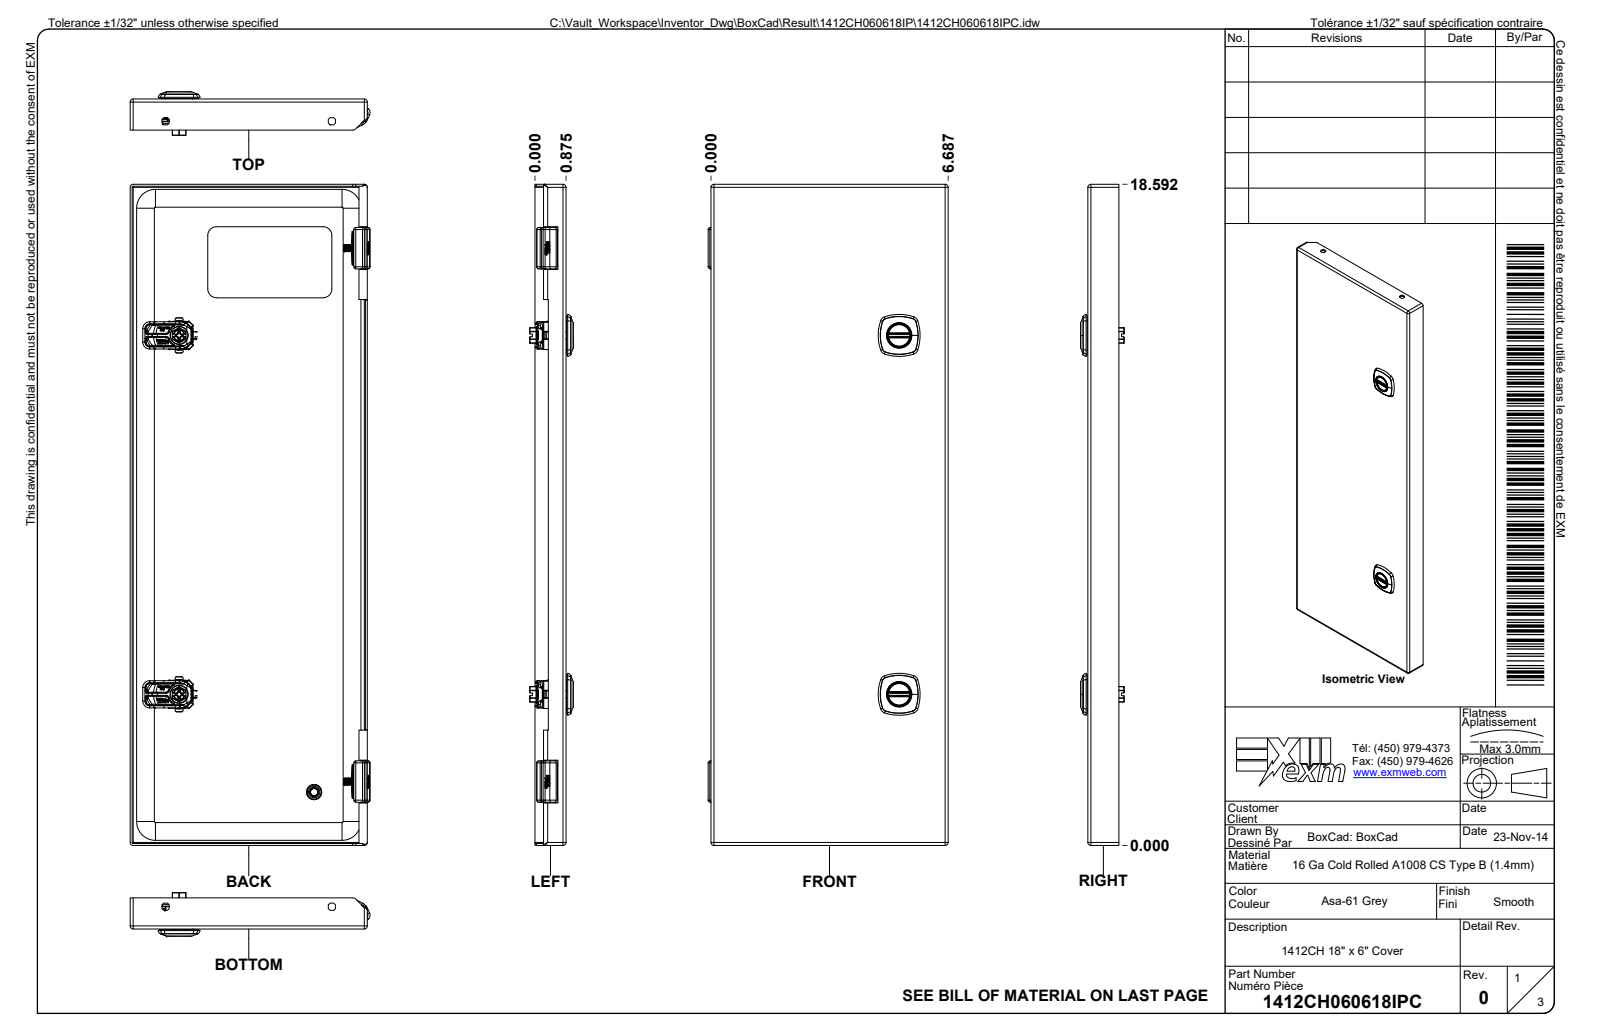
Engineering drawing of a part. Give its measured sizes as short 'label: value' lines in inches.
name: 1412CH060618IP; 1412CH060618IPB; 1412CH060618IPB-P; STK-Q-08350 (+8 more)
written by: Autodesk Inventor 2024 (AUTOMOTIVE_DESIGN)
unit: in
bodies: 67 solids, 9235 faces (4701 planar, 1930 cylindrical, 2604 other)
size: 18.592 × 7.496 × 6.451
volume: 42.74 in³; area: 1 447 in²
holes: 13× ⌀0.201, 6× ⌀0.03, 6× ⌀0.24, 6× ⌀0.311, 4× ⌀0.305, 4× ⌀0.32, 4× ⌀0.394, 2× ⌀0.165, 2× ⌀0.173, 2× ⌀0.175, 2× ⌀0.236, 2× ⌀0.63
bosses: 10× ⌀0.232, 6× ⌀0.512, 6× ⌀0.035, 4× ⌀0.39, 3× ⌀0.197, 2× ⌀0.799, 2× ⌀0.626, 2× ⌀0.504
rounds: 293× R0.02, 105× R0.01, 94× R0.008, 91× R0.012, 82× R0.039, 53× R0.004, 31× R0.079, 31× R0.197
face distances: 0.055, 5.945, 6.126, 6, 5.89, 6.181, 6.071, 0.413, 0.469, 5.658
hole spacings: 1.275, 4.67, 4.67, 15.502, 15.502, 14.87, 16.139, 2.088
